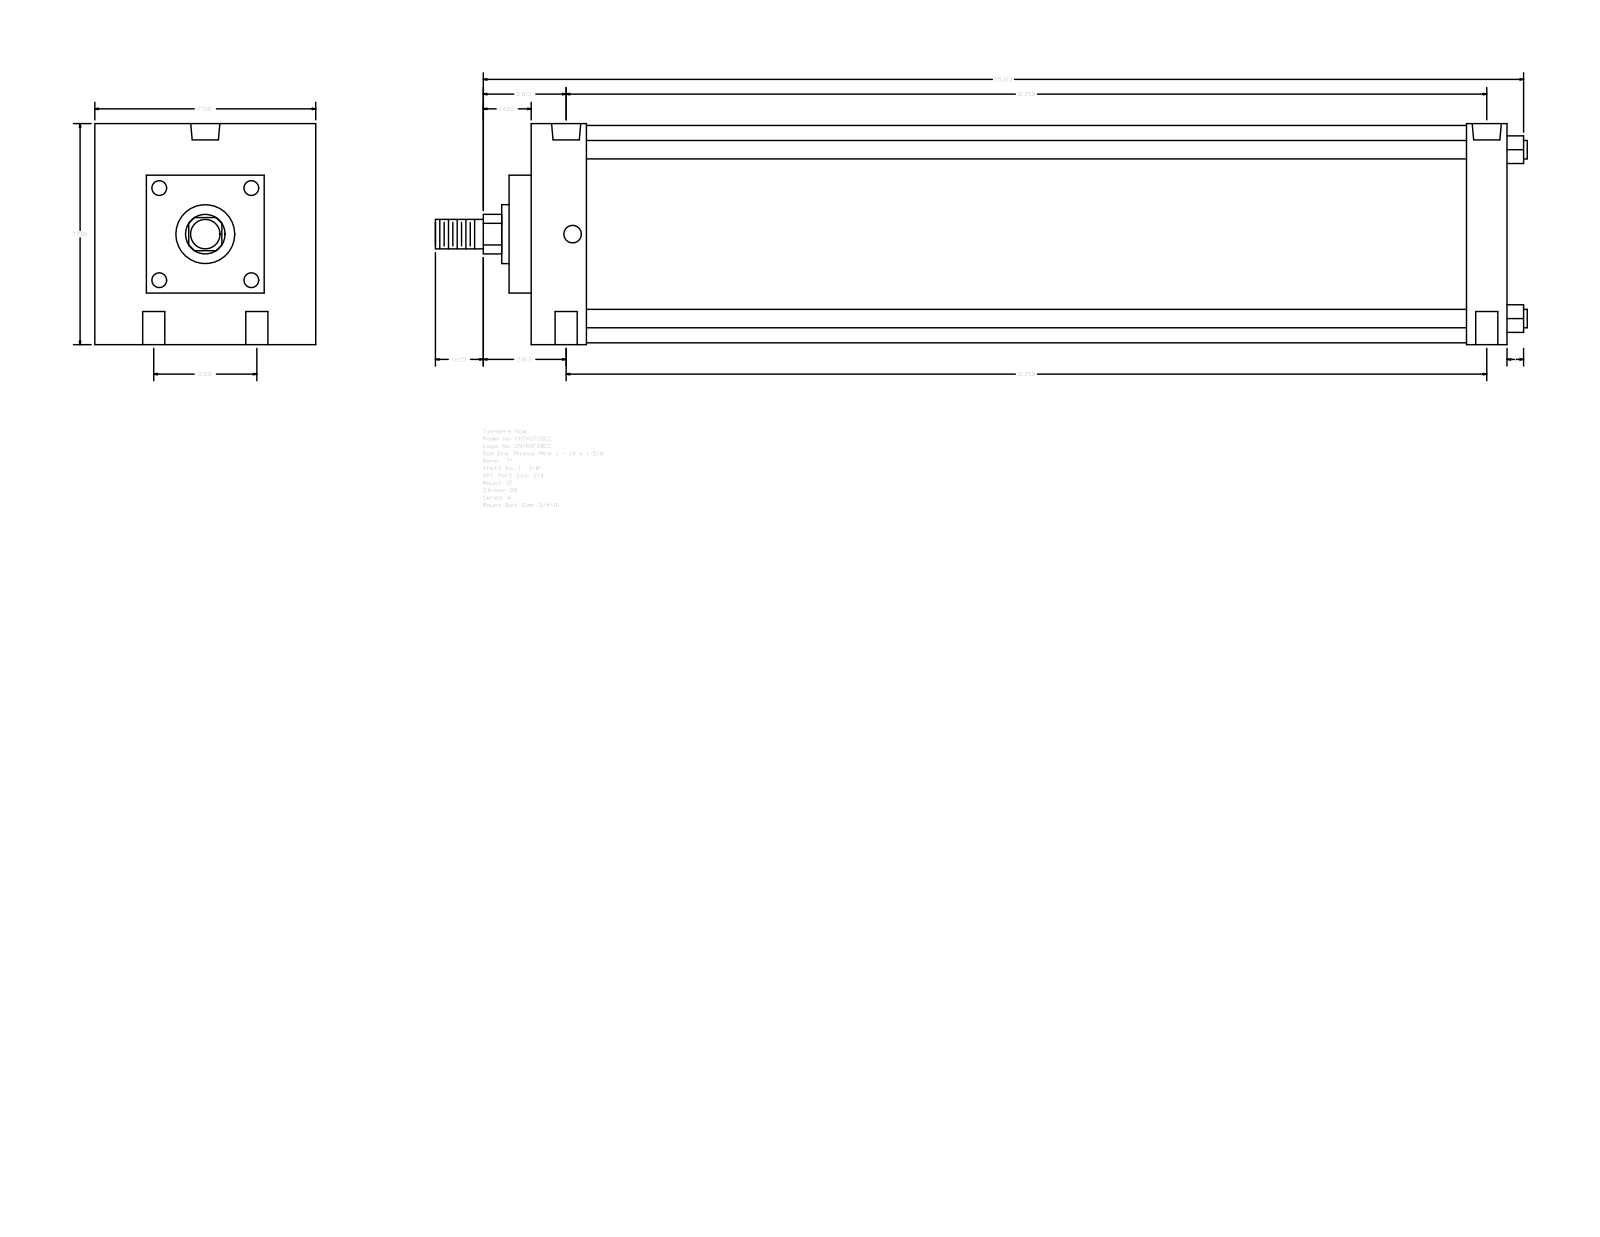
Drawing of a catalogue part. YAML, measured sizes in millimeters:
part_name: "A_SF__0700_1.375"
step_written_by: "GSSL Pune (CONFIG_CONTROL_DESIGN)"
units: millimeters
bodies: {solids: 0, faces: 93, planar: 67, cylindrical: 26, other: 0}
overall_size: [941.39, 190.5, 190.5]
round_holes:
  - {diameter: 19.05, count: 4}
  - {diameter: 15.08, count: 2}
  - {diameter: 25.12, count: 2}
round_bosses_or_shafts:
  - {diameter: 15.88, count: 4}
  - {diameter: 187.32, count: 1}
  - {diameter: 50.8, count: 1}
  - {diameter: 34.92, count: 1}
  - {diameter: 25.4, count: 1}
partial_cylinders:
  - {radius: 17.06, count: 1}
face_to_face_distances: [190.5, 841.38, 19.04, 860.42, 66.67, 825.5, 47.63, 806.46, 758.83, 793.75]
hole_center_spacings: [44.45, 794.99, 793.75, 88.9, 798.71, 782.63]
